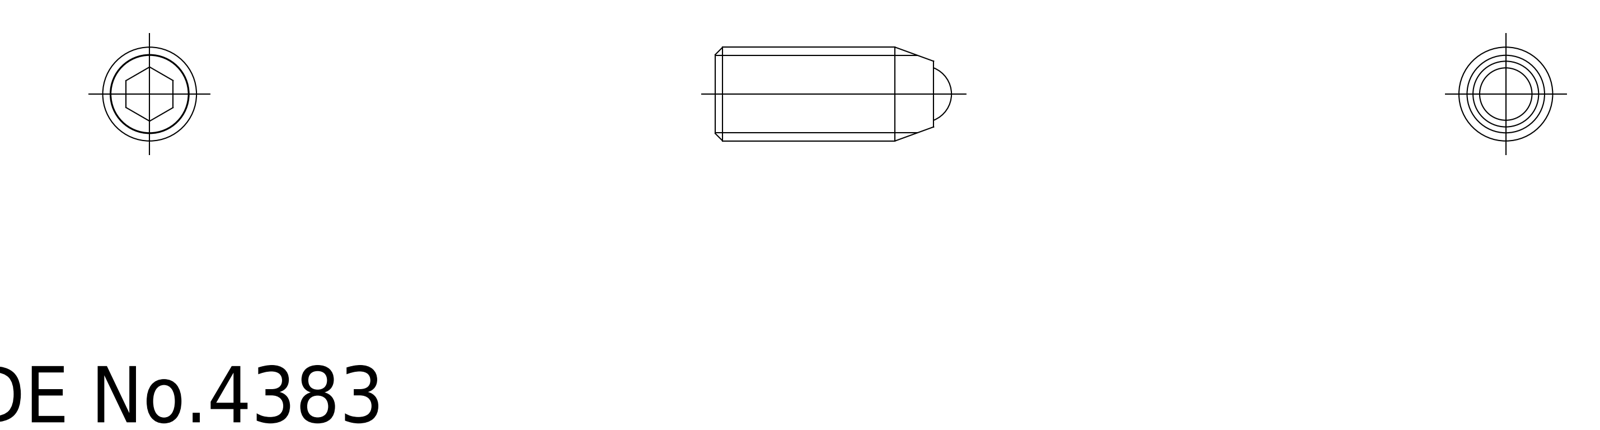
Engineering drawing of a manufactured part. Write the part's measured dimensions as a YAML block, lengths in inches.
part_name: "ball; SCS_M5_12_R_17068_36"
step_written_by: "CADfix (AUTOMOTIVE_DESIGN)"
units: inches
bodies: {solids: 2, faces: 20, planar: 0, cylindrical: 0, other: 20}
overall_size: [0.496, 0.197, 0.197]
volume: 0.012
surface_area: 0.453
